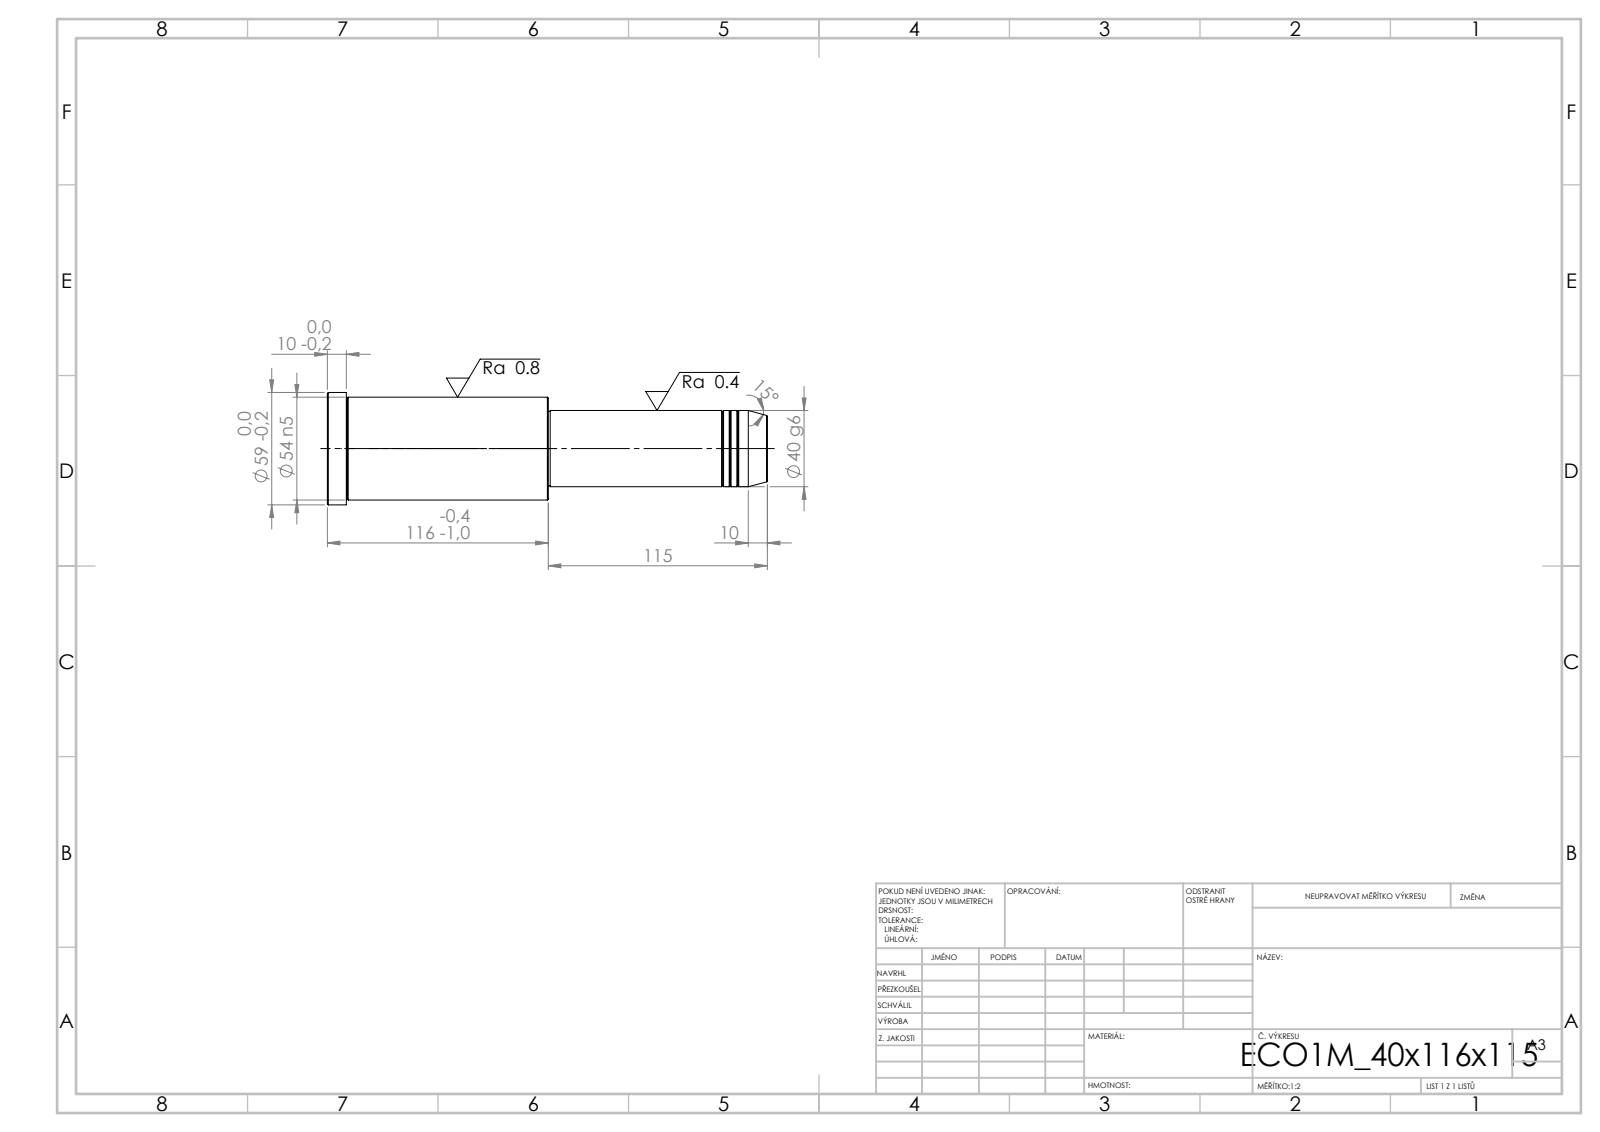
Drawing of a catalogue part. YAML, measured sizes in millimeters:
step_written_by: "SolidWorks 2019 (CONFIG_CONTROL_DESIGN)"
units: millimeters
bodies: {solids: 1, faces: 43, planar: 5, cylindrical: 14, other: 24}
overall_size: [231, 59, 59]
volume: 412686
surface_area: 39702
round_bosses_or_shafts:
  - {diameter: 59, count: 1}
  - {diameter: 54, count: 1}
  - {diameter: 40, count: 1}
  - {diameter: 39, count: 1}
face_to_face_distances: [116, 115, 231, 221, 106, 10, 114, 1, 107, 117]
